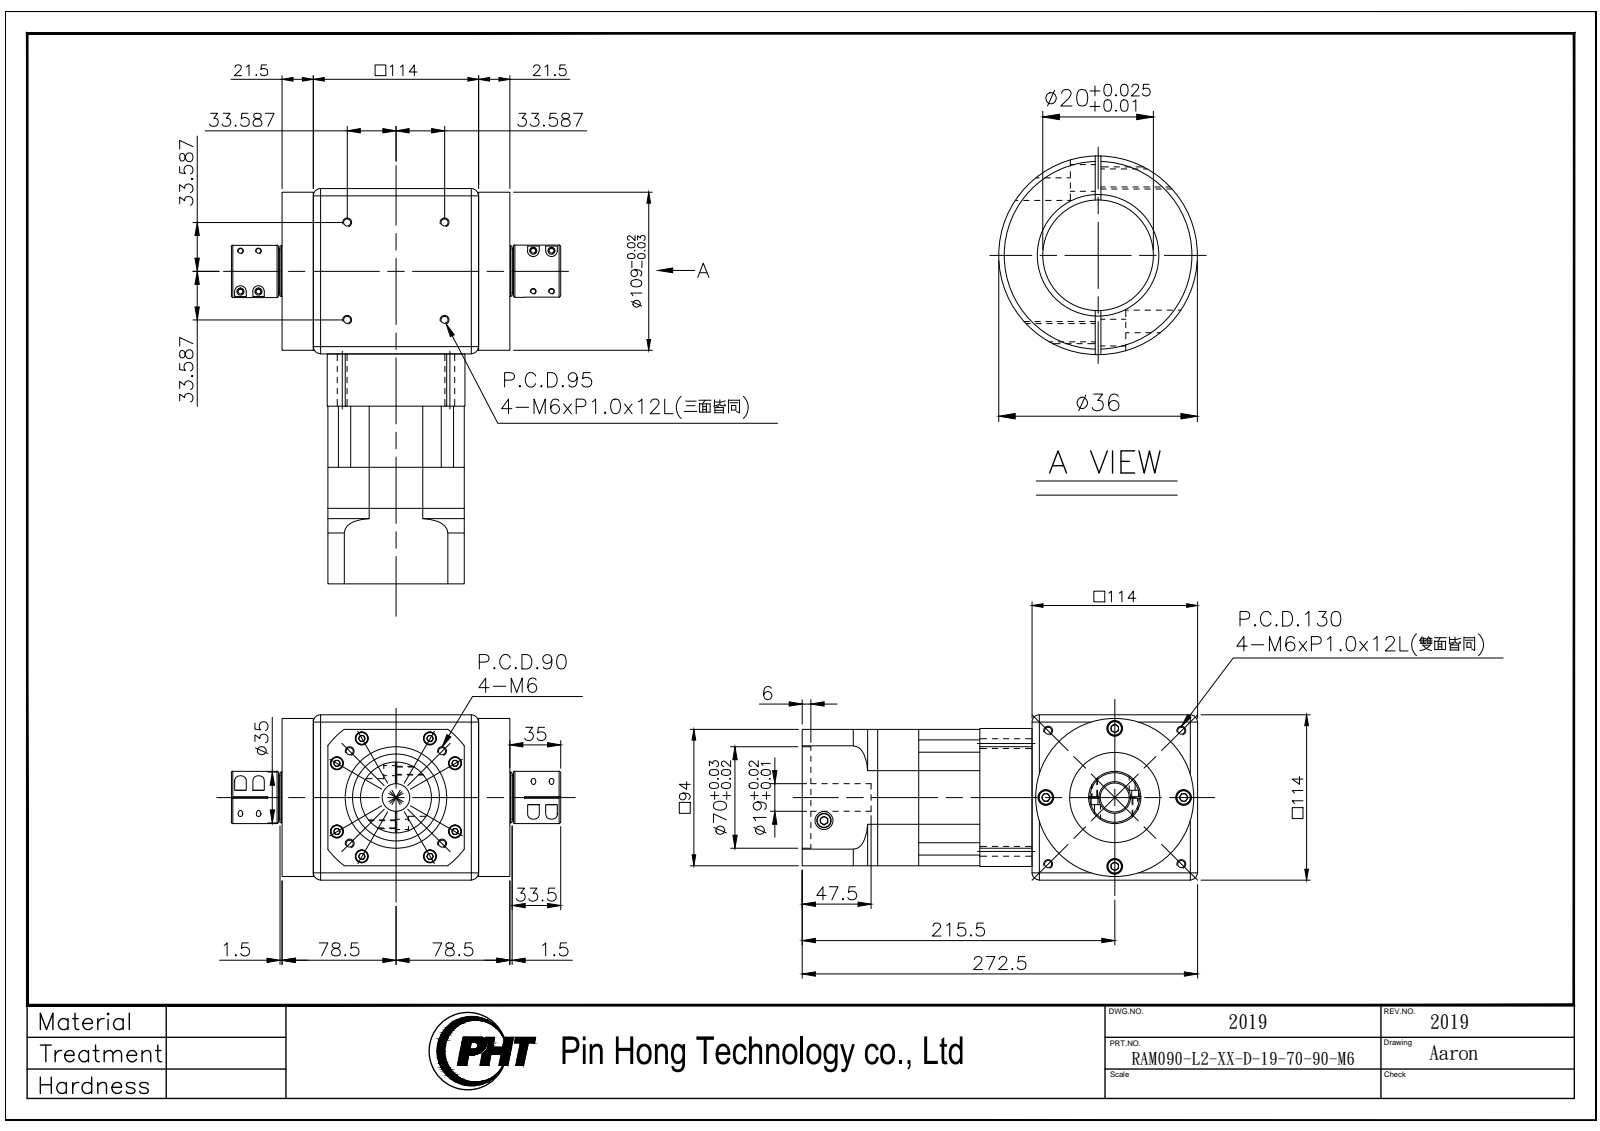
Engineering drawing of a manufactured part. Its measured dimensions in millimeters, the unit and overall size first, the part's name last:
Units: millimetres
Overall size (bounding box): 272.5 × 227 × 114
Round holes (diameter × count): ⌀5 ×16, ⌀5.2 ×8, ⌀6 ×8, ⌀9 ×8, ⌀6.6 ×4, ⌀6.8 ×4, ⌀11 ×4, ⌀12.7 ×2, ⌀19 ×1, ⌀20 ×1, ⌀27 ×1, ⌀28 ×1
Round bosses / shafts (diameter × count): ⌀8.5 ×16, ⌀10 ×8, ⌀9.2 ×8, ⌀5 ×8, ⌀109 ×1, ⌀80 ×1, ⌀62 ×1, ⌀49 ×1
Partial cylindrical surfaces — rounded edges, fillets, slot ends (radius × count): R4.75 ×8, R2.55 ×4, R6 ×4, R50.5 ×1, R59 ×1, R79.1 ×1
Main face-to-face distances: 114, 10, 104, 106.5, 28.3, 78.2, 220.5, 192.2, 94, 31.5
Hole centre spacings: 47, 67.18, 12.17, 12.34, 14.08, 45.99, 47.5, 56.03
Volume: 3 009 000 mm³ · Surface area: 277 183 mm²
Bodies: 4 solids, 1017 faces (502 planar, 340 cylindrical, 175 other)
Part name (STEP PRODUCT): RAM090-L2-XX-D-19-70-90-M6_2019
STEP written by: SolidWorks 2016 (AUTOMOTIVE_DESIGN)
